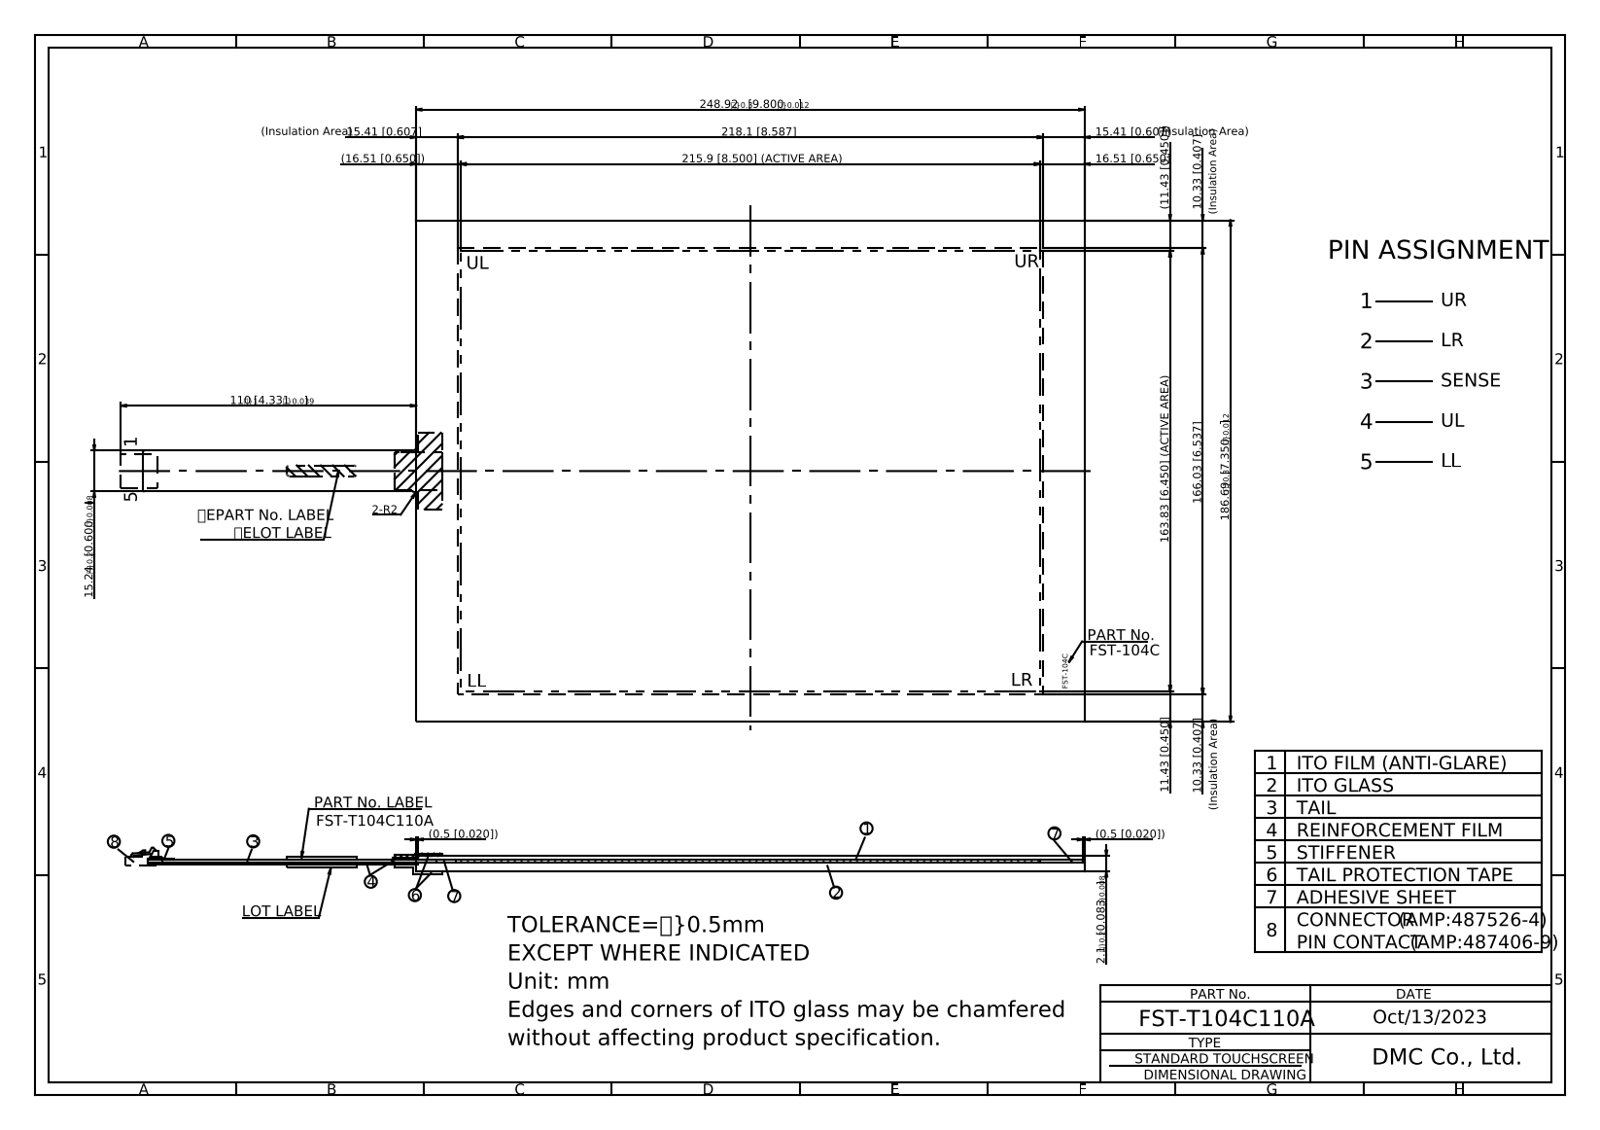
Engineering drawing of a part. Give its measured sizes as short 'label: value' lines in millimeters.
name: FST-T104C110A
written by: Autodesk Inventor 2020 (AUTOMOTIVE_DESIGN)
unit: mm
bodies: 1 solid, 43 faces (43 planar, 0 cylindrical, 0 other)
size: 408.71 × 261.37 × 3.15
volume: 94 482 mm³; area: 98 271 mm²
face distances: 2, 2.1, 1.8, 1.9, 186.68, 248.92, 0.65, 0.75, 0.85, 1.15
